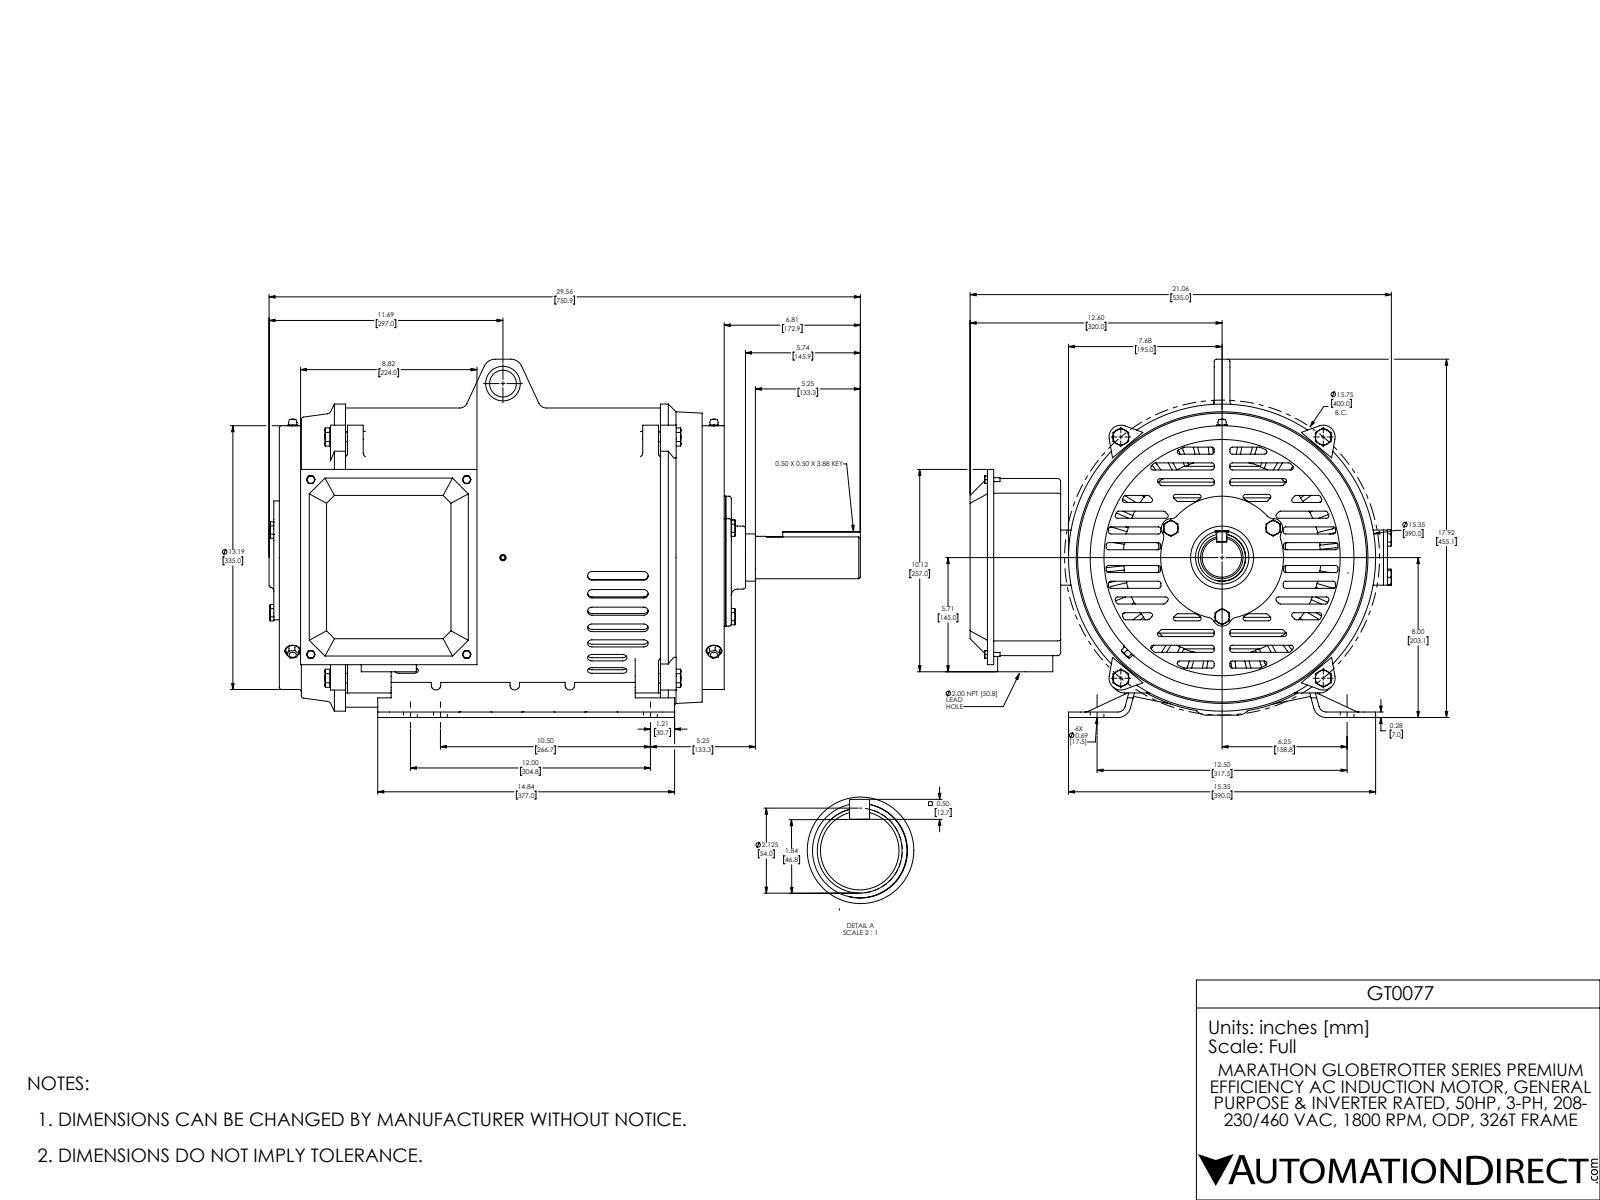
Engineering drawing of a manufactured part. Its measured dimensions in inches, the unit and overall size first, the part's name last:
Units: inches
Overall size (bounding box): 29.563 × 21.063 × 17.917
Round holes (diameter × count): ⌀0.394 ×14, ⌀0.236 ×10, ⌀0.374 ×10, ⌀0.197 ×9, ⌀0.268 ×8, ⌀0.315 ×7, ⌀0.685 ×6, ⌀0.276 ×5, ⌀0.528 ×4, ⌀0.787 ×4, ⌀0.118 ×2, ⌀0.157 ×2
Round bosses / shafts (diameter × count): ⌀0.472 ×4, ⌀0.197 ×4, ⌀0.315 ×3, ⌀0.394 ×2, ⌀15.354 ×1, ⌀14.173 ×1, ⌀13.189 ×1, ⌀11.85 ×1
Partial cylindrical surfaces — rounded edges, fillets, slot ends (radius × count): R0.118 ×234, R0.217 ×52, R0.268 ×48, R0.276 ×36, R0.029 ×18, R0.088 ×18, R0.157 ×16, R0.394 ×14
Main face-to-face distances: 0.059, 0.079, 0.276, 6.772, 4.528, 0.787, 4.469, 7.52, 1.575, 4.449
Hole centre spacings: 4.821, 6.299, 8.908, 11.639, 1.969, 1.392, 2.648, 2.756
Volume: 977.6 in³ · Surface area: 5 687 in²
Bodies: 68 solids, 3593 faces (1365 planar, 1474 cylindrical, 754 other)
Part name (STEP PRODUCT): SS620746-326T_Rev0 r1 1face r1 -Rbell red1 COMPLETE Coord
STEP written by: SolidWorks 2017 (AUTOMOTIVE_DESIGN)
